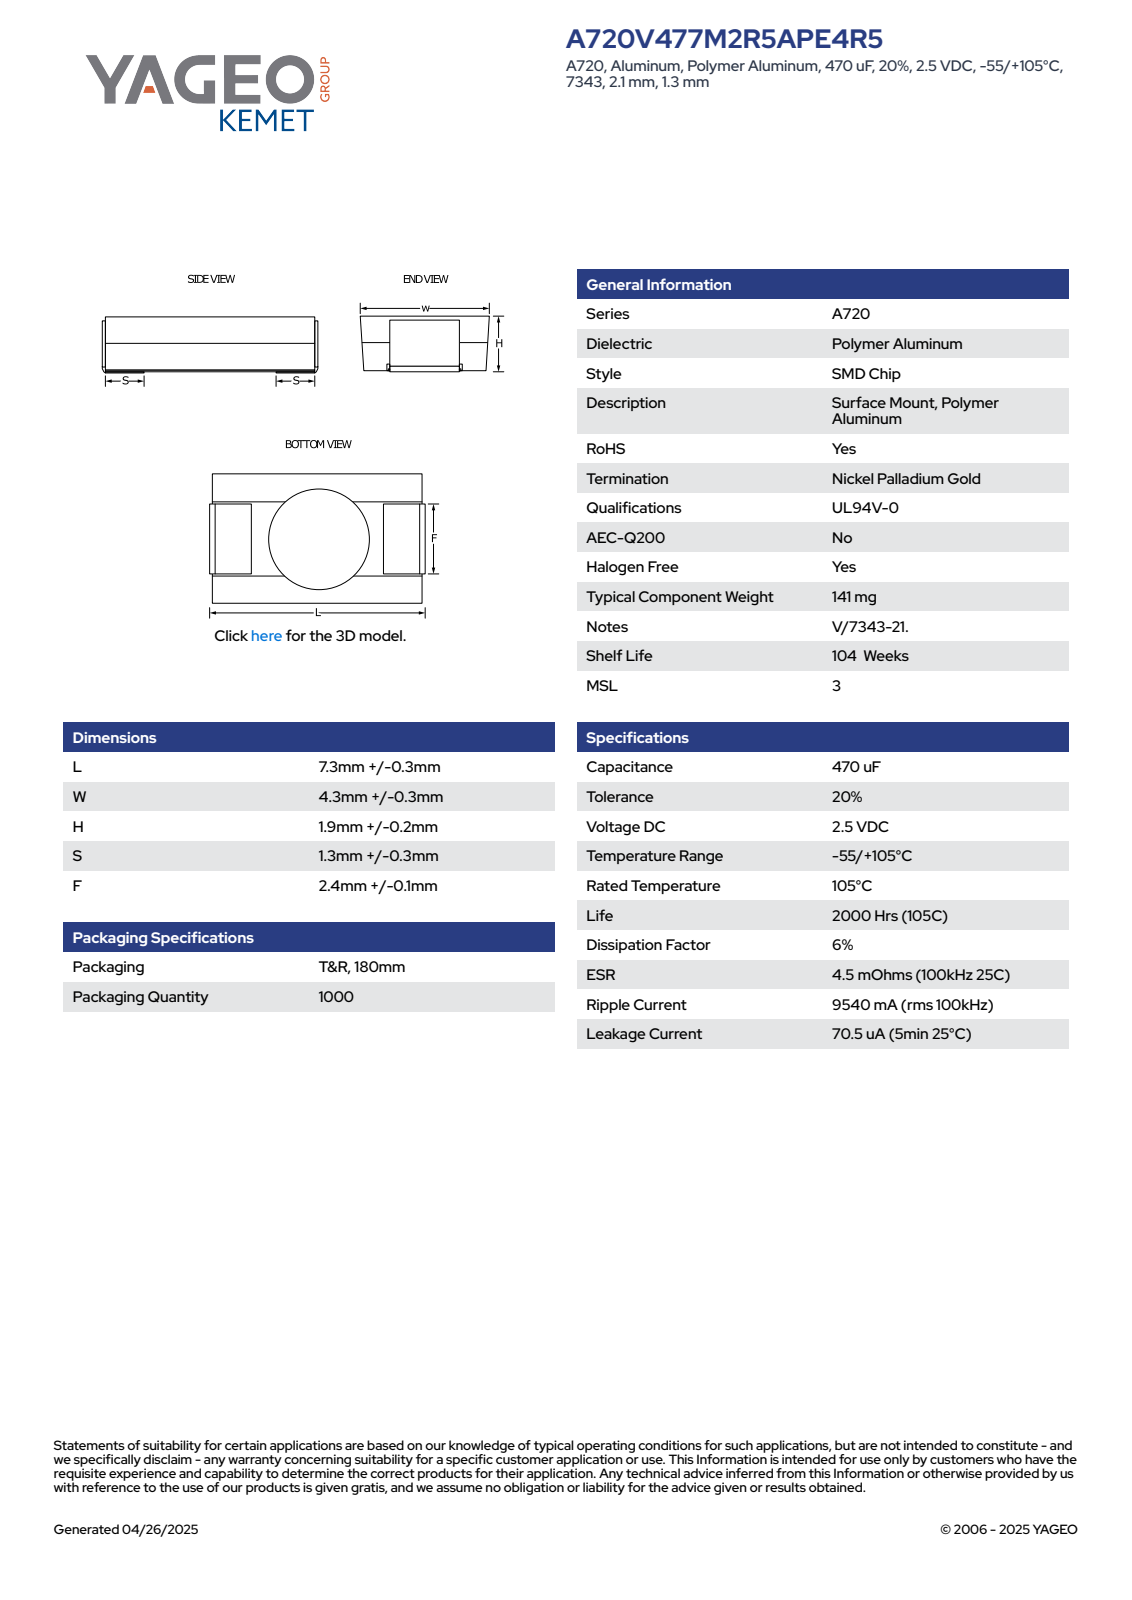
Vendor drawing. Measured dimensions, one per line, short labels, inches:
name: CAS_SMD2_L7.6W4.6H2.1S1.3F2.5
written by: SolidWorks 2020 (AUTOMOTIVE_DESIGN)
unit: in
bodies: 1 solid, 96 faces (90 planar, 6 cylindrical, 0 other)
size: 0.299 × 0.181 × 0.169
volume: 0.008 in³; area: 0.295 in²
bosses: 1× ⌀0.149
rounds: 4× R0.004
face distances: 0.18, 0.169, 0.289, 0.295, 0.165, 0.291, 0.299, 0.167, 0.17, 0.168
